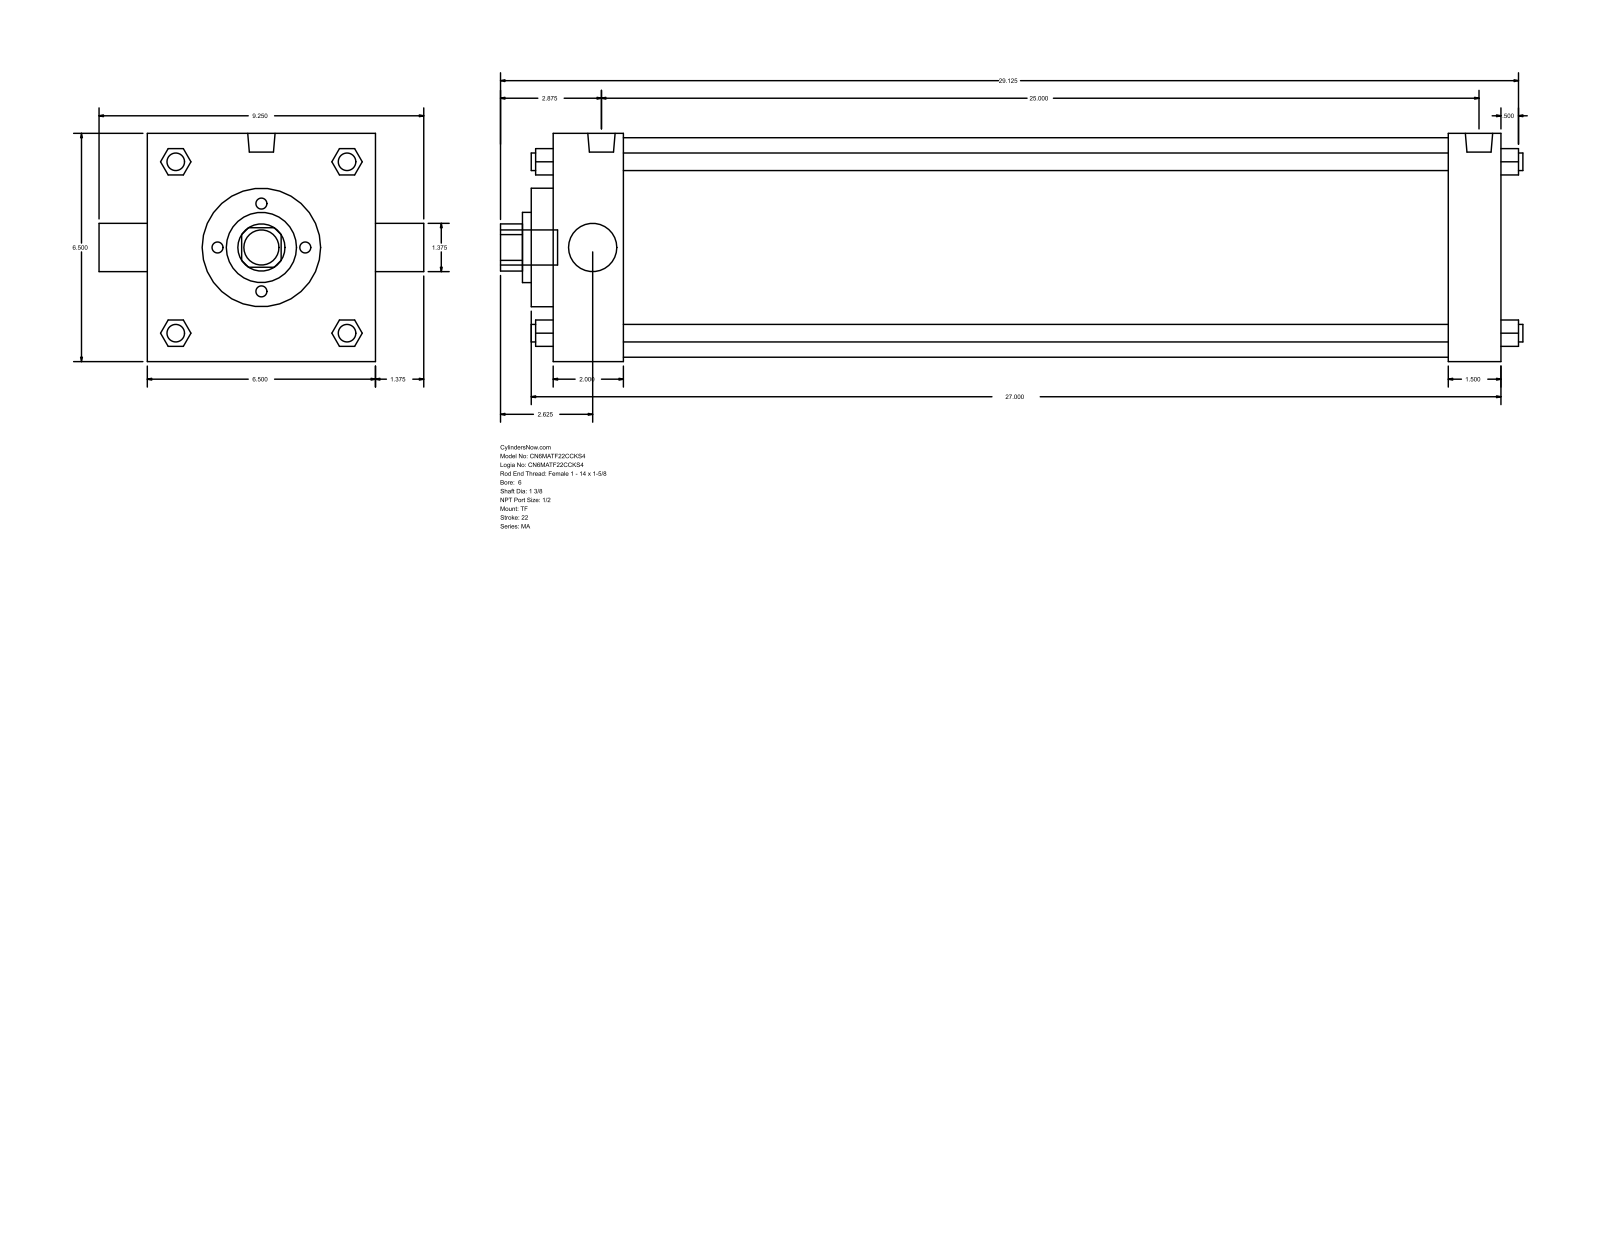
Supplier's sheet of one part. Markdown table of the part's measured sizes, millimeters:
| quantity | value |
| --- | --- |
| part name | MA_TF__0600_1.375 |
| STEP written by | GSSL Pune (CONFIG_CONTROL_DESIGN) |
| units | millimeters |
| bodies | 0 solids, 122 faces (93 planar, 29 cylindrical, 0 other) |
| overall size | 739.77 × 234.95 × 165.1 |
| round holes (diameter × count) | 34.92 × 2, 50.8 × 1, 85.72 × 1, 158.75 × 1 |
| round bosses / shafts (diameter × count) | 12.7 × 4, 17.46 × 3, 19.77 × 2, 25.4 × 1 |
| partial cylindrical surfaces (radius × count) | 17.06 × 1 |
| main face-to-face distances | 165.1, 688.98, 38.1, 50.8, 638.18, 650.88, 600.08, 15.87, 66.67, 666.75 |
